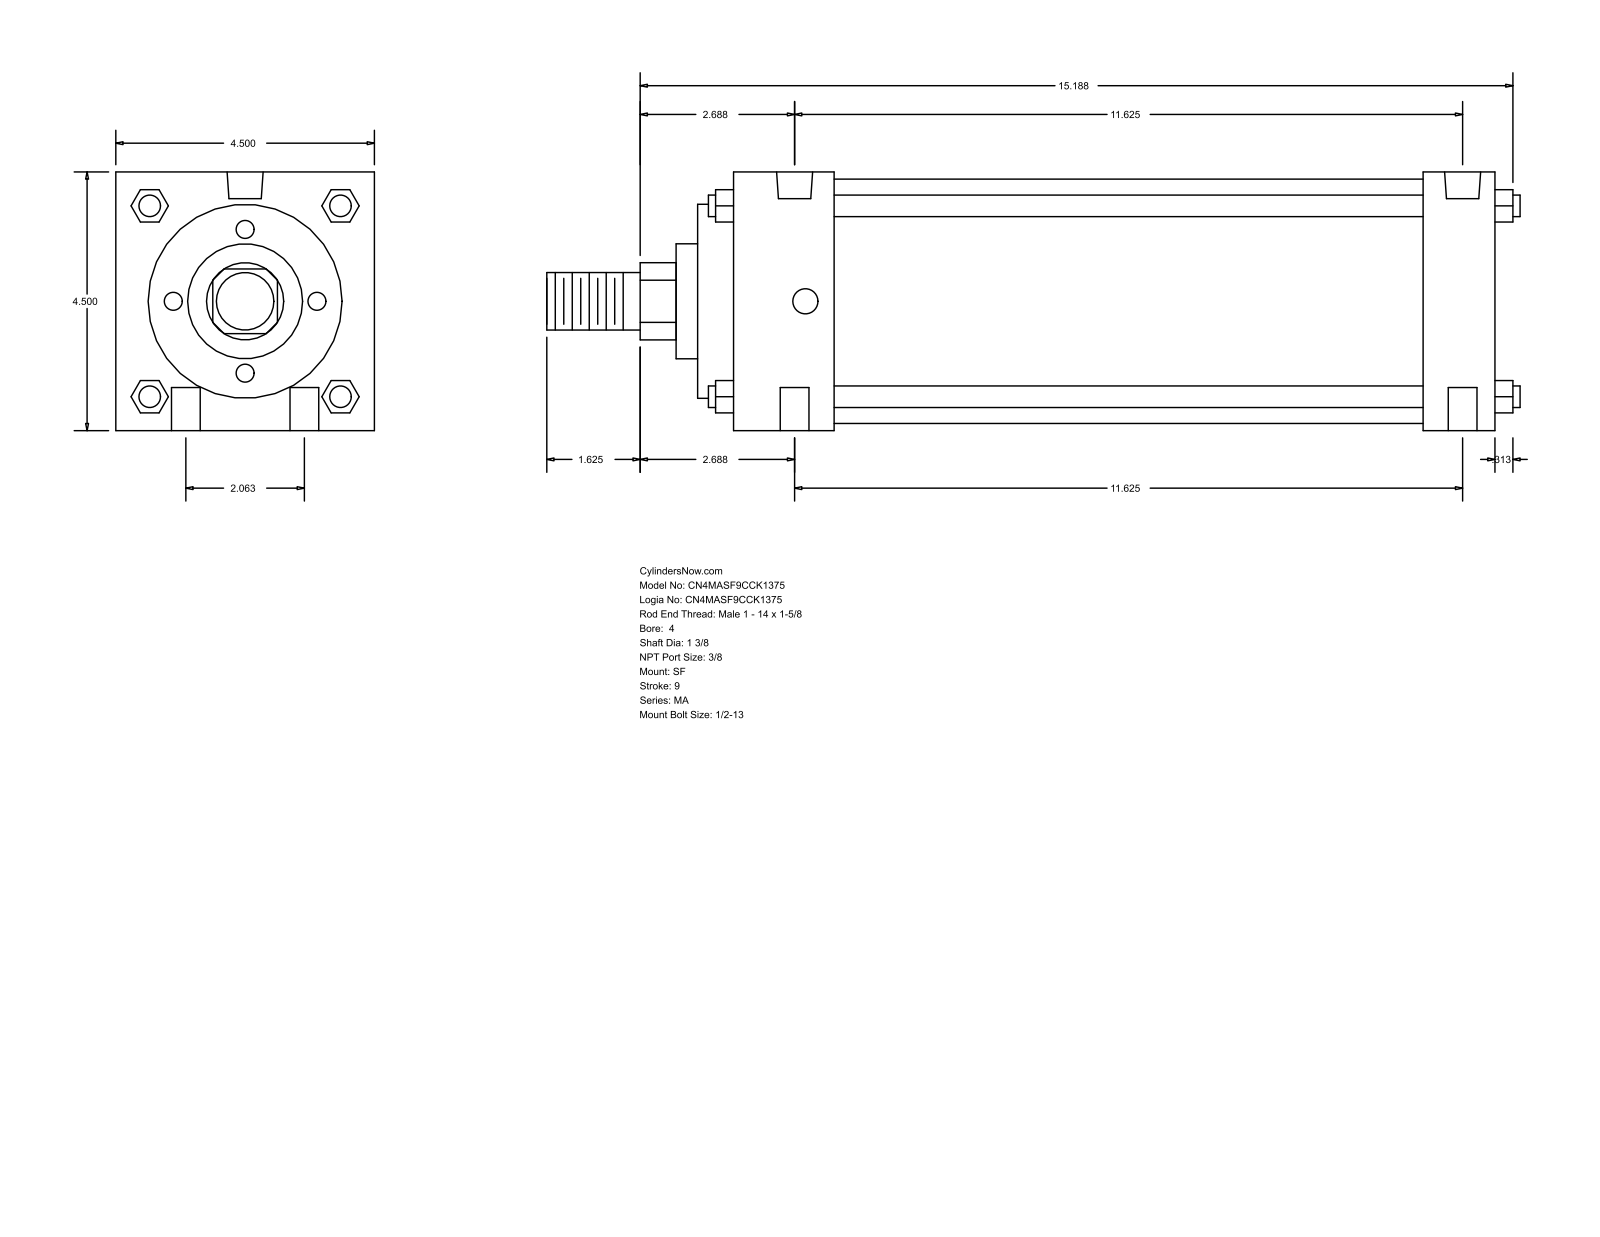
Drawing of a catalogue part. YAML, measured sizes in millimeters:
part_name: "MA_SF__0400_1.375"
step_written_by: "GSSL Pune (CONFIG_CONTROL_DESIGN)"
units: millimeters
bodies: {solids: 0, faces: 126, planar: 95, cylindrical: 31, other: 0}
overall_size: [430.21, 114.3, 114.3]
round_holes:
  - {diameter: 12.7, count: 4}
  - {diameter: 11.11, count: 2}
  - {diameter: 15.93, count: 2}
round_bosses_or_shafts:
  - {diameter: 9.53, count: 4}
  - {diameter: 107.95, count: 1}
  - {diameter: 85.72, count: 1}
  - {diameter: 50.8, count: 1}
  - {diameter: 34.92, count: 1}
  - {diameter: 25.4, count: 1}
partial_cylinders:
  - {radius: 17.06, count: 1}
face_to_face_distances: [114.3, 336.55, 352.42, 15.87, 320.67, 304.8, 31.75, 60.32, 44.45, 260.35]
hole_center_spacings: [26.19, 296.44, 295.28, 52.38, 299.89, 285.74]
